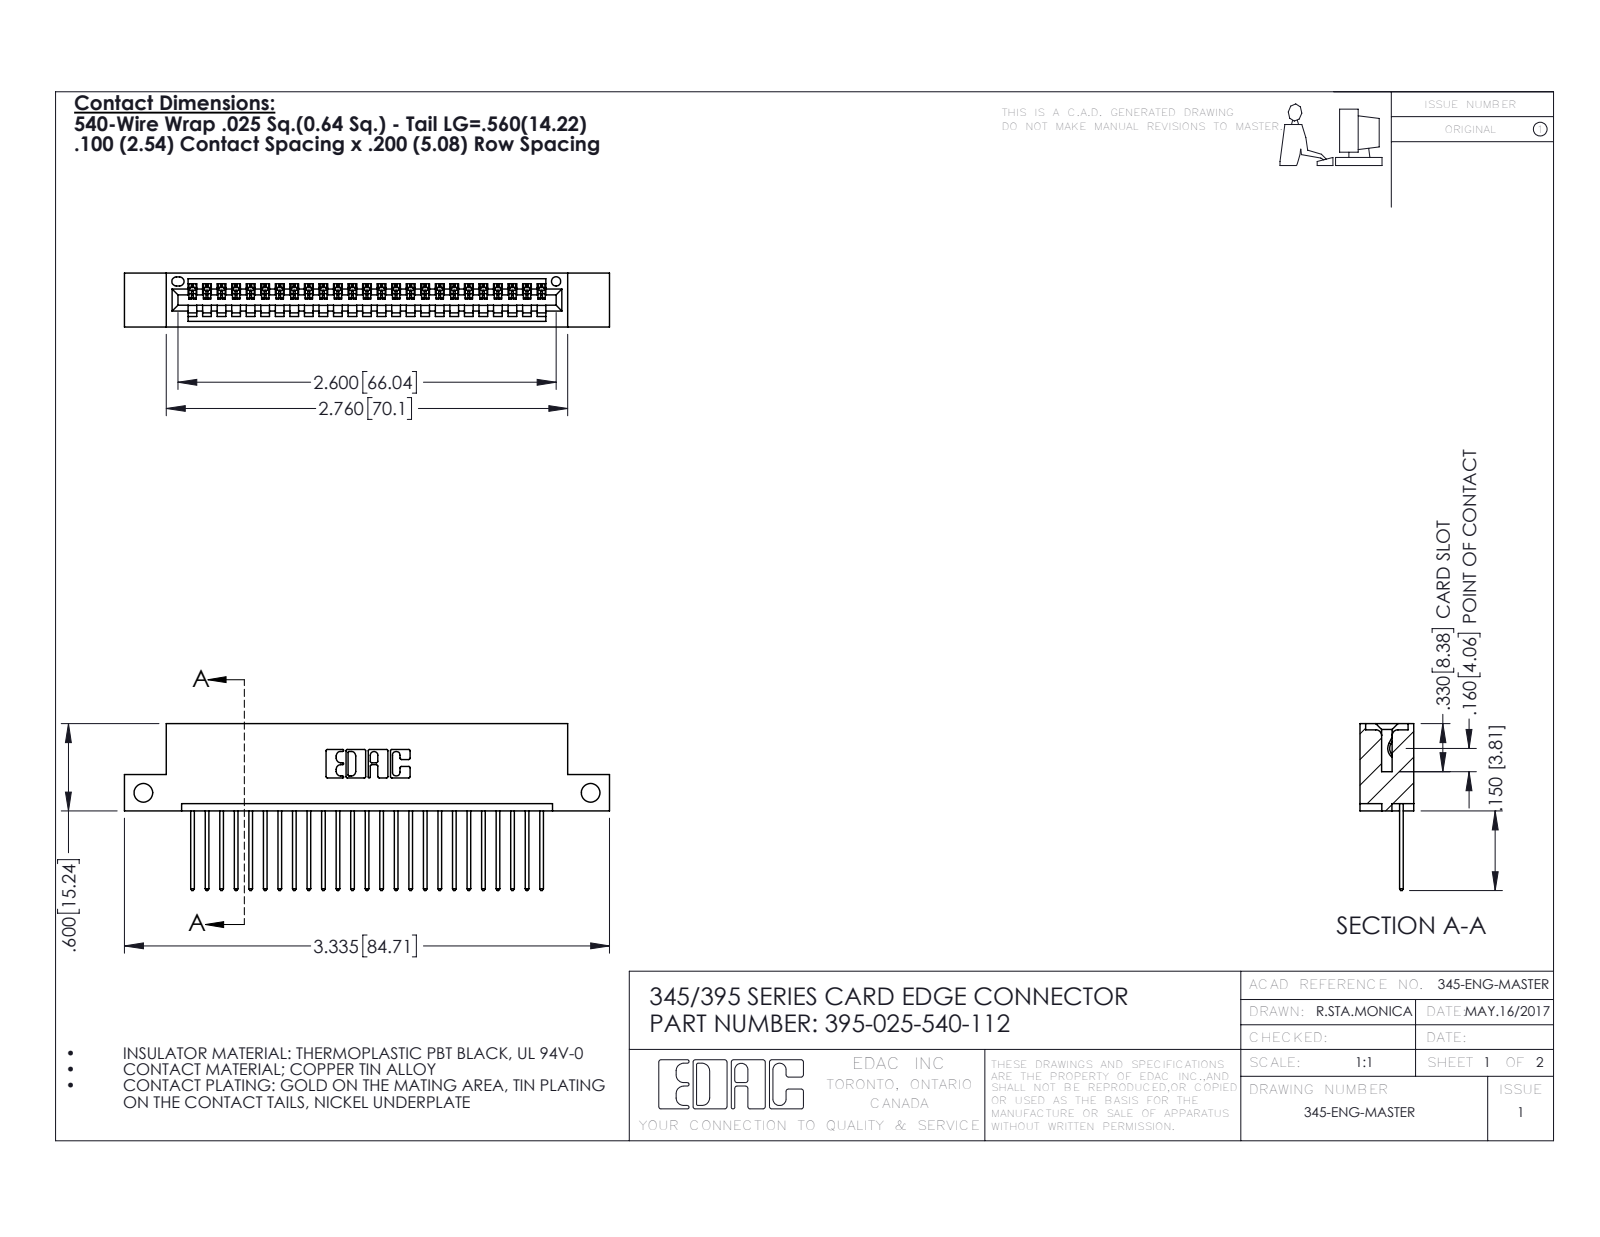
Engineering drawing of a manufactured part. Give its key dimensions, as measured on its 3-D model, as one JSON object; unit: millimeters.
{"part_name": "345-292-001_345-293-140; 345 Part_Flush Mounting Lugs - Side Mount; 395-025-540-112", "step_written_by": "SolidWorks 2016 (CONFIG_CONTROL_DESIGN)", "units": "millimeters", "bodies": {"solids": 26, "faces": 1576, "planar": 1080, "cylindrical": 496, "other": 0}, "overall_size": [84.7, 29.1, 9.4], "volume_mm3": 7850, "surface_area_mm2": 10310, "round_holes": [[3.3, 2], [1.6, 1]], "partial_cylinders_radius": [[0.2, 50], [0.3, 50], [0.3, 22], [0.2, 6], [0.8, 6], [0.7, 3], [0.8, 2], [1, 2]], "face_to_face_distances": [7.6, 1.8, 5.1, 9.4, 2.5, 6.9, 0.6, 5.7, 3.8, 1.8], "hole_center_spacings": [78.1]}
